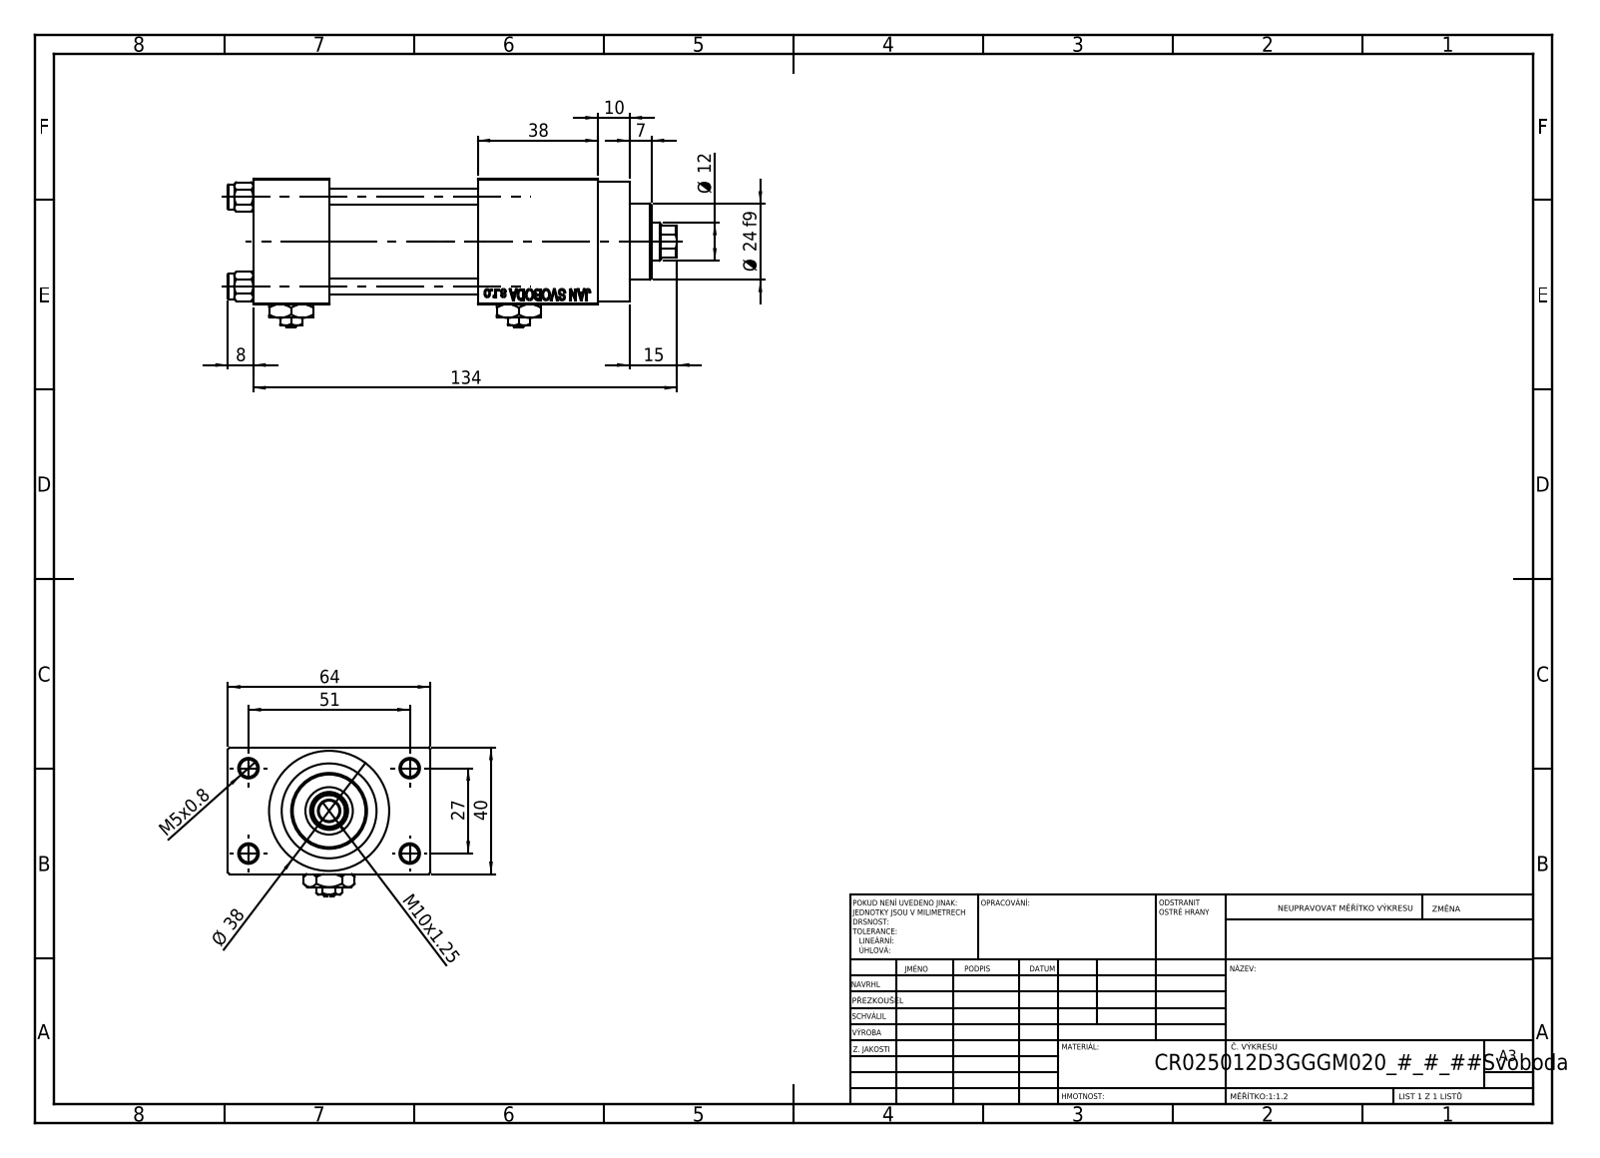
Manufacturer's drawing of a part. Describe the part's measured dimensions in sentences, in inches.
The part is named "V215CR_D_Body; Zatka_pro_OIL_PORT; V215CR_VCP_D; NUT_M5_D (+2 more)". Its 3-D file was written by "SolidWorks 2019 (CONFIG_CONTROL_DESIGN)". It is 13 solids with 1202 faces: 542 planar, 100 cylindrical and 560 other. Overall it measures 5.591 by 2.52 by 1.85 inches. Its volume is 10.63 cubic inches and its surface area 98.14 square inches. Round holes: 4 of diameter 0.197, 4 of diameter 0.217, 3 of diameter 0.787, 2 of diameter 0.276, 2 of diameter 0.518, 1 of diameter 0.256, 1 of diameter 0.472, 1 of diameter 0.591, 1 of diameter 0.984, 1 of diameter 1.181. Round bosses or shafts: 4 of diameter 0.315, 1 of diameter 1.496, 1 of diameter 1.22, 1 of diameter 0.945. Partial cylindrical surfaces (rounded edges, fillets, slot ends): 1 of radius 0.217. The main face-to-face distances are 1.575, 2.047, 0.472, 1.85, 0.945, 2.795, 2.52, 1.496, 3.346, 4.291. The hole center spacings are 0.448, 0.788, 1.114, 1.136, 1.177, 1.561, 1.903, 1.063.
